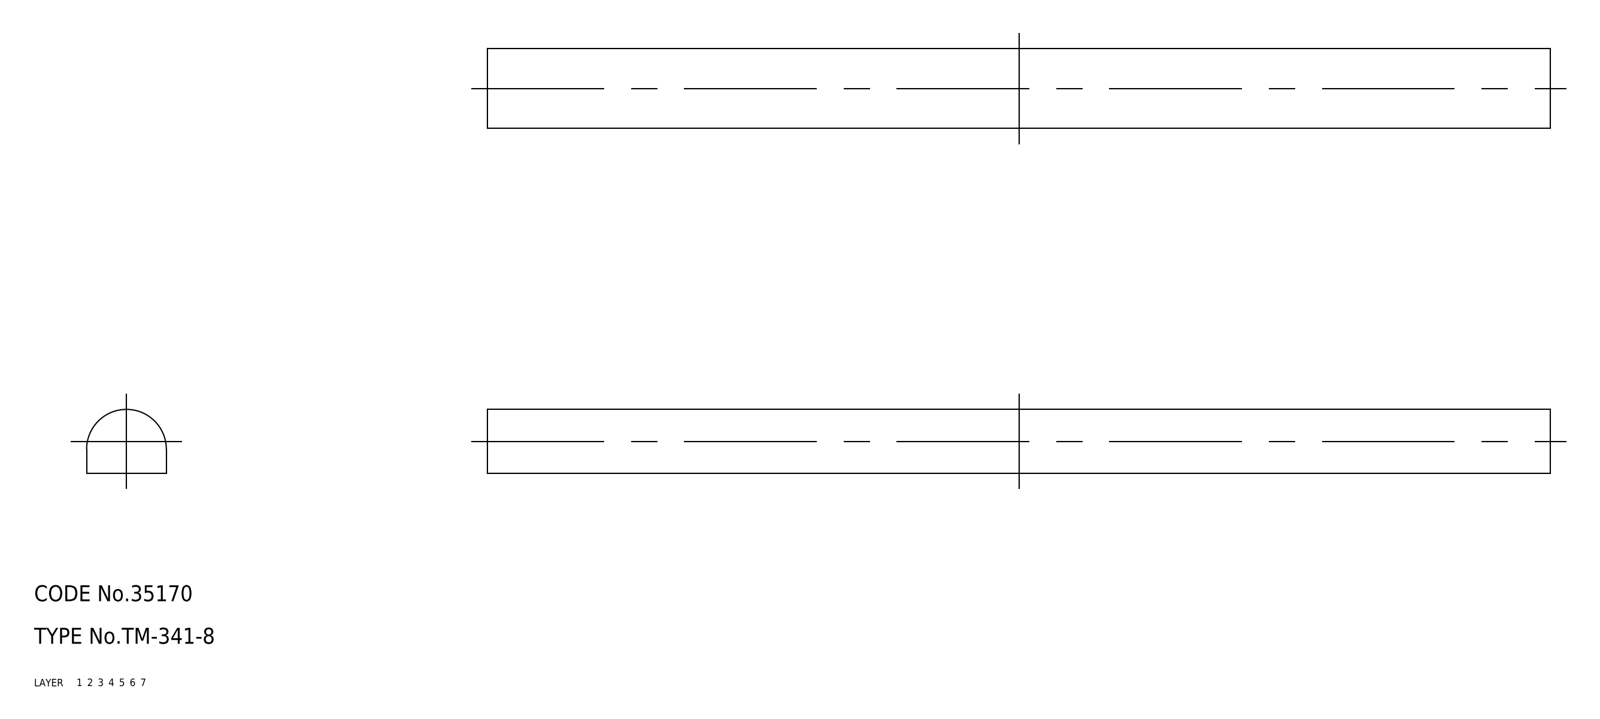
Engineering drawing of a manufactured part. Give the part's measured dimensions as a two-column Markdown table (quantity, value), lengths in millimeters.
| quantity | value |
| --- | --- |
| part name | TM_341_8; rubber foam |
| STEP written by | SolidWorks 2015 (AUTOMOTIVE_DESIGN) |
| units | millimeters |
| bodies | 1 solid, 6 faces (5 planar, 1 cylindrical, 0 other) |
| overall size | 200 × 15 × 12 |
| volume | 31 171 mm³ |
| surface area | 9 824 mm² |
| partial cylindrical surfaces (radius × count) | 7.5 × 1 |
| main face-to-face distances | 15, 200 |
